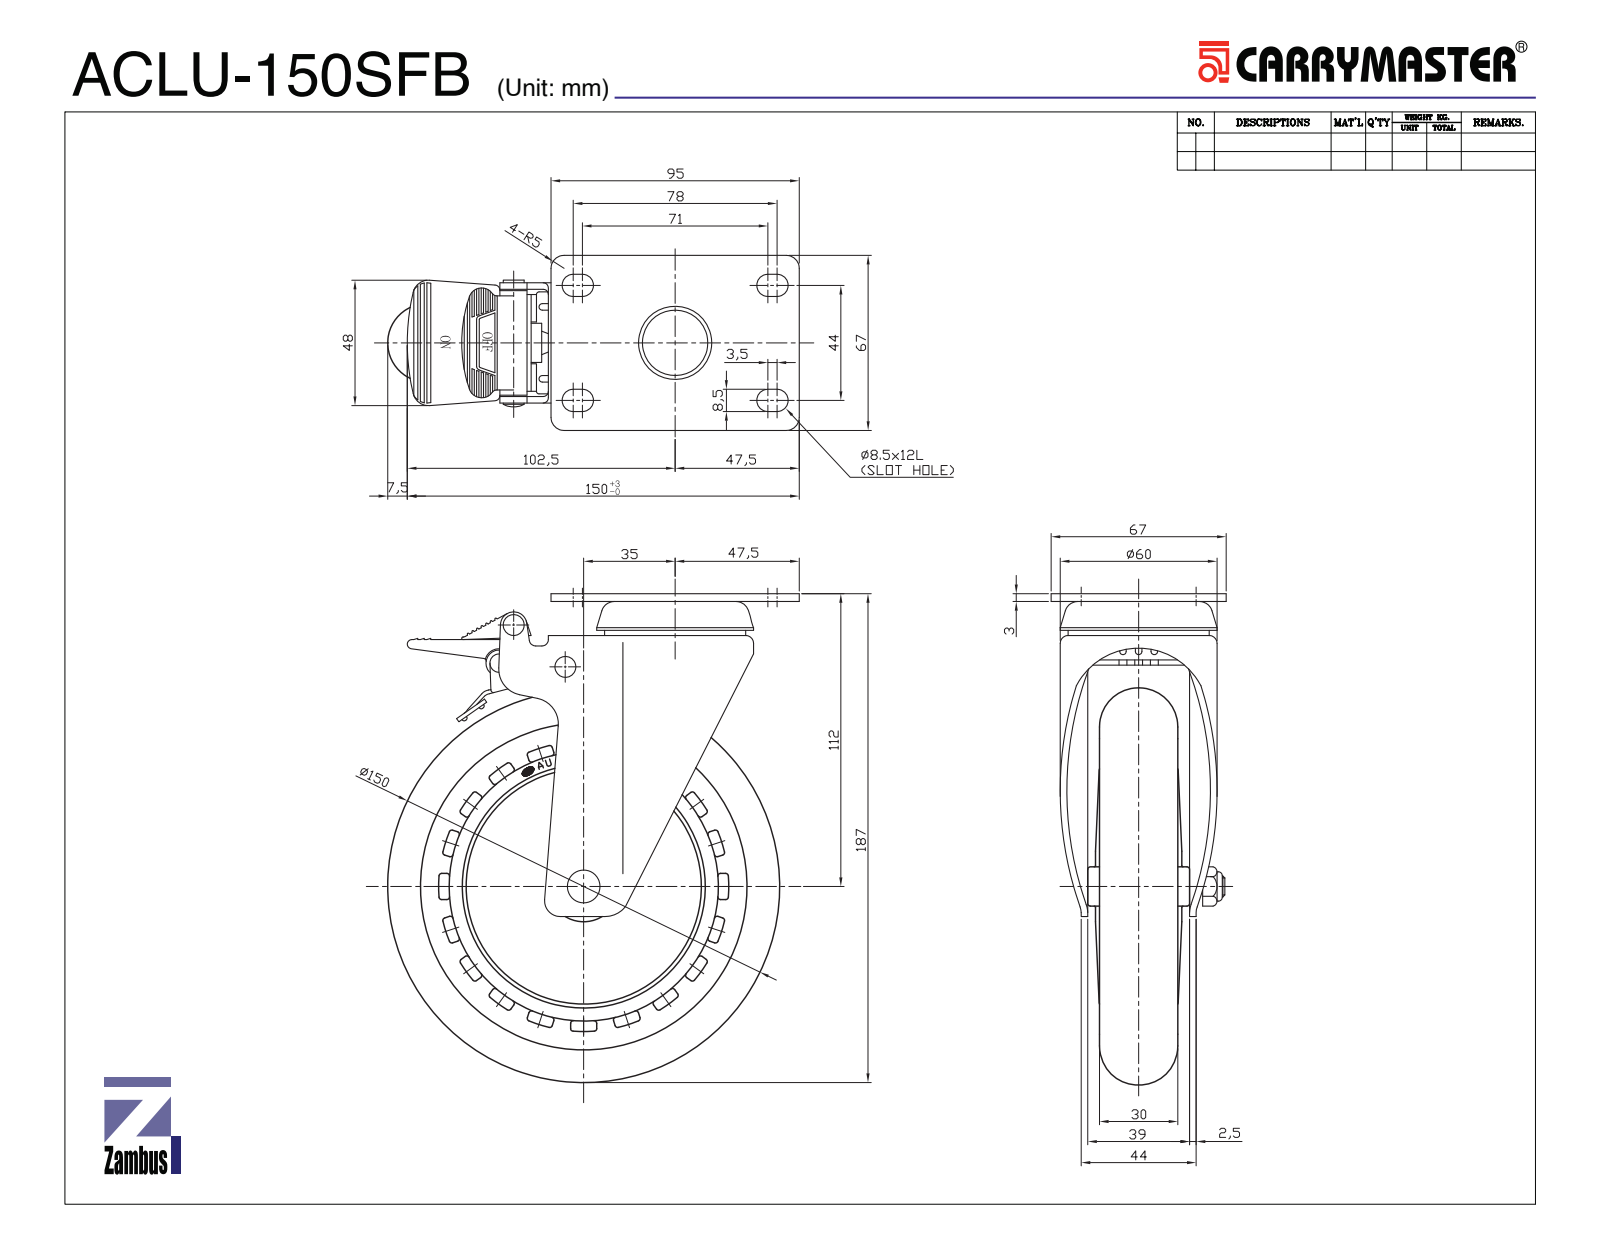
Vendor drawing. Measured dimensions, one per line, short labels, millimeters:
name: ACLU-150SFB
written by: SolidWorks 2015 (CONFIG_CONTROL_DESIGN)
unit: mm
bodies: 23 solids, 1619 faces (837 planar, 482 cylindrical, 300 other)
size: 186.45 × 159 × 69.56
volume: 484 109 mm³; area: 198 772 mm²
holes: 2× ⌀3.5, 2× ⌀4.3, 2× ⌀5.2, 1× ⌀5.3, 1× ⌀6.8, 1× ⌀8, 1× ⌀9.6, 1× ⌀12.6, 1× ⌀19.6, 1× ⌀22, 1× ⌀28.62, 1× ⌀29.82
bosses: 2× ⌀9, 2× ⌀4.9, 1× ⌀120, 1× ⌀90, 1× ⌀59.7, 1× ⌀32, 1× ⌀21.5, 1× ⌀16
rounds: 91× R1, 20× R0.2, 19× R3.86, 16× R46.25, 6× R2, 6× R6, 4× R2.5, 4× R3
face distances: 30.5, 12.3, 18.7, 0.5, 5, 2.5, 11.8, 18.2, 7.5, 5.5
hole spacings: 9.7, 12.81, 17.54, 17.62, 25.74, 26.08, 84.49, 89.39
